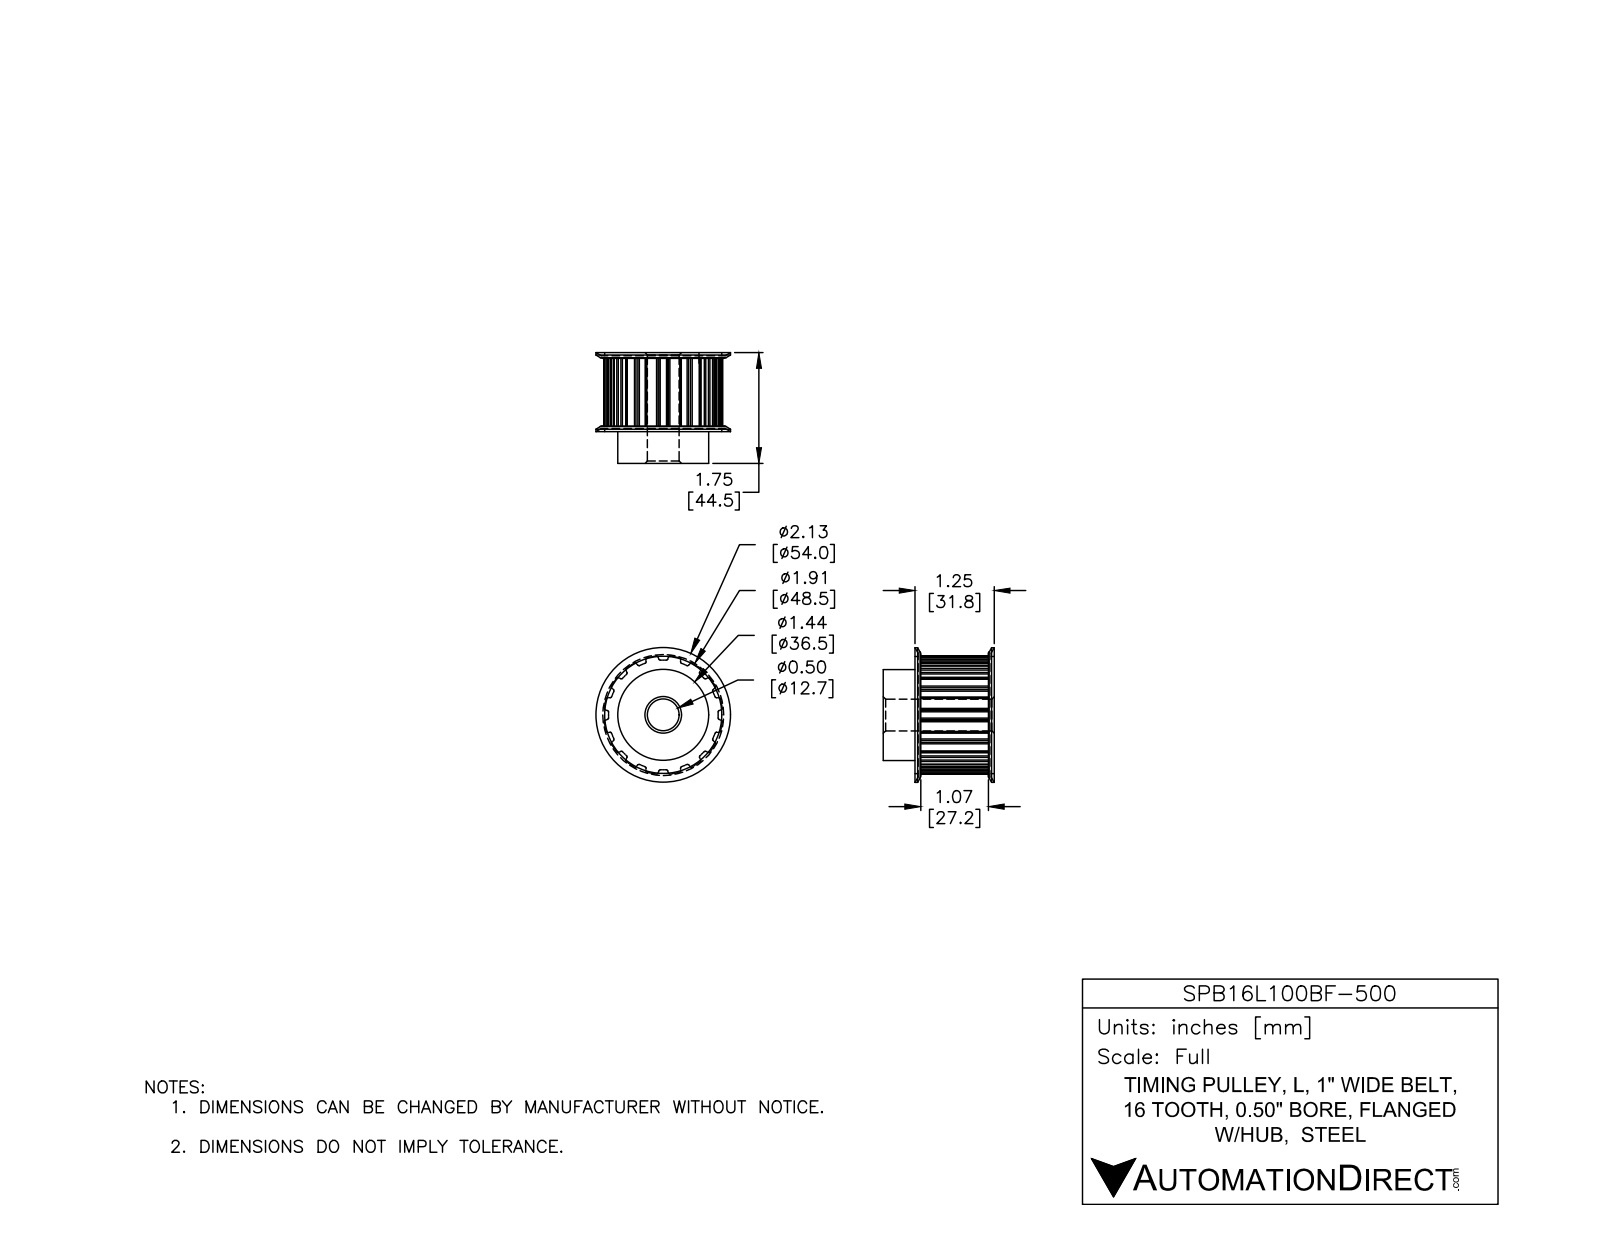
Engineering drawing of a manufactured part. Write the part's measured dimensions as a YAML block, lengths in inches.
part_name: "SPB16L100BF-500"
step_written_by: "SolidWorks 2015 (AUTOMOTIVE_DESIGN)"
units: inches
bodies: {solids: 1, faces: 177, planar: 55, cylindrical: 106, other: 16}
overall_size: [2.125, 2.125, 1.75]
volume: 3.792
surface_area: 22.73
round_holes:
  - {diameter: 0.5, count: 1}
round_bosses_or_shafts:
  - {diameter: 2.125, count: 1}
  - {diameter: 2.125, count: 1}
  - {diameter: 1.849, count: 1}
  - {diameter: 1.437, count: 1}
partial_cylinders:
  - {radius: 0.02, count: 64}
  - {radius: 0.94, count: 1}
face_to_face_distances: [1.75, 1.25, 0.5, 0.05, 1.2, 0.09, 1.16, 0.04, 1.11, 1.73]
